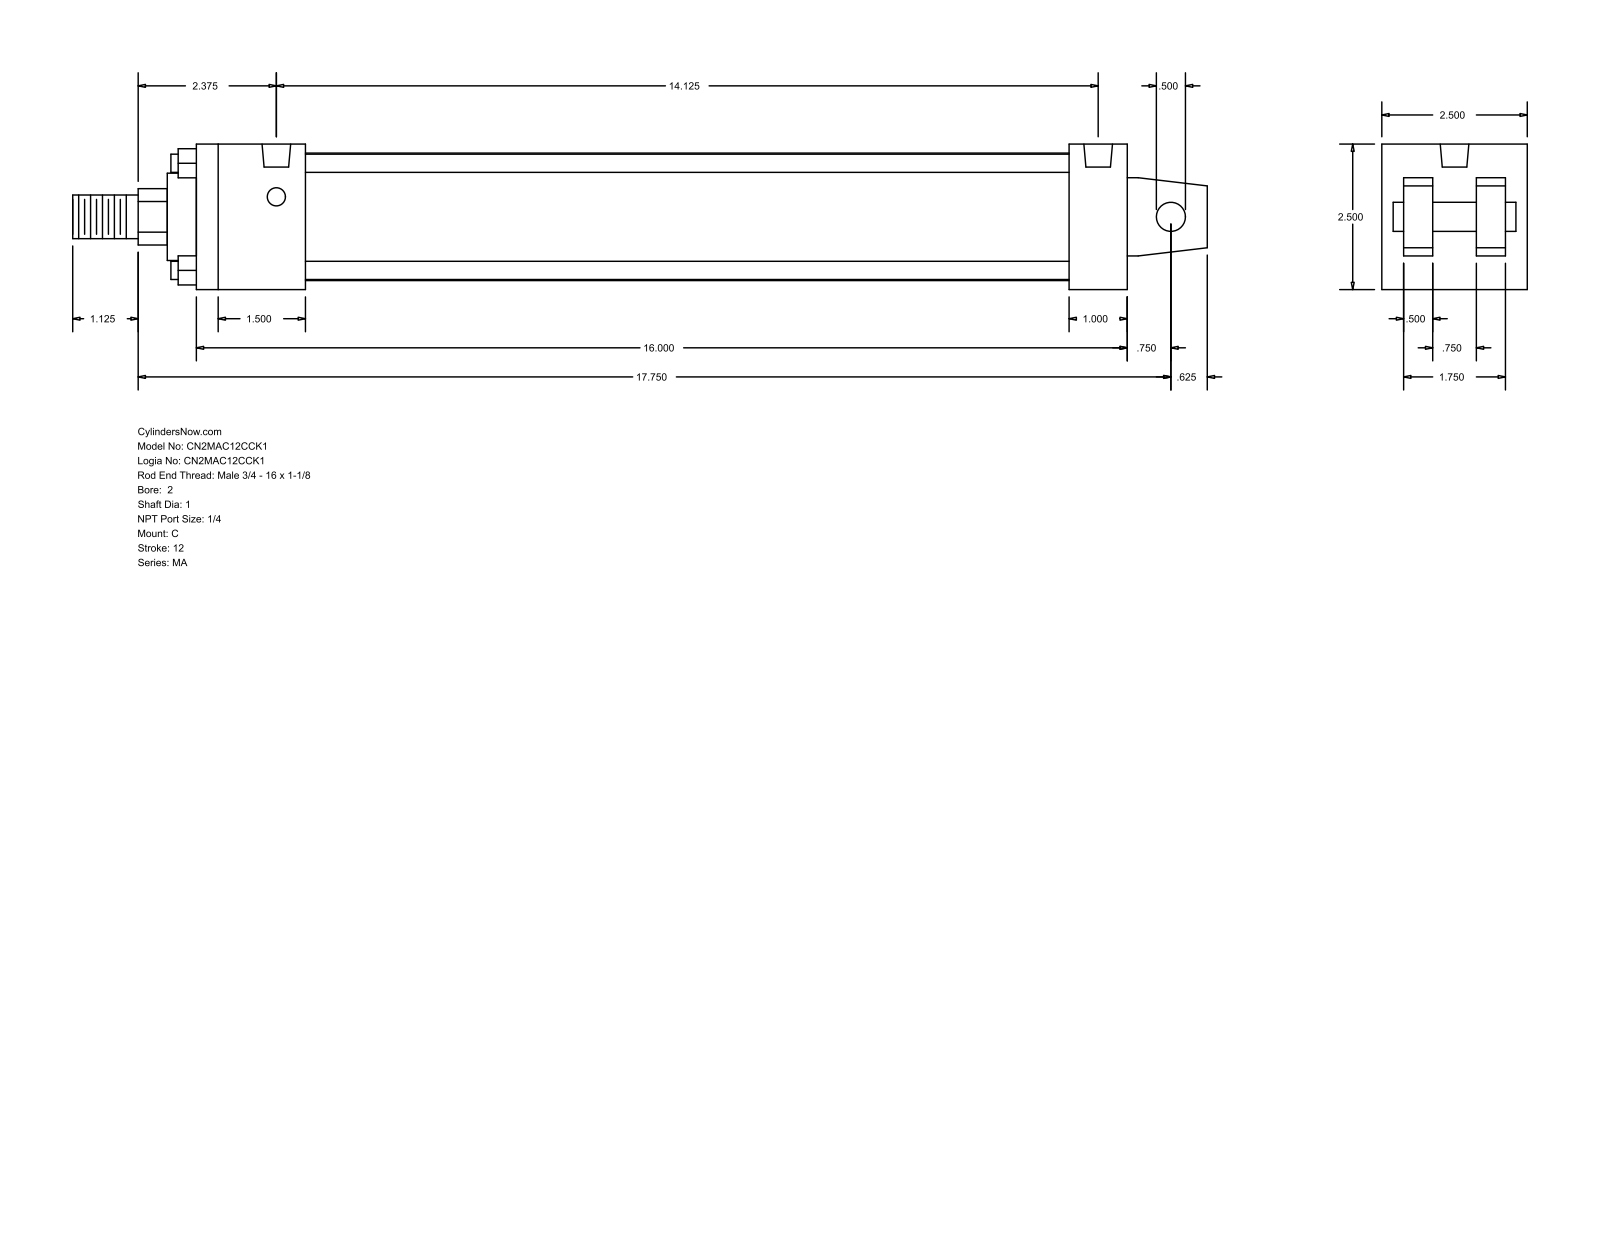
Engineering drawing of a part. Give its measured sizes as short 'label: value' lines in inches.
name: MA_C__0200_1
written by: GSSL Pune (CONFIG_CONTROL_DESIGN)
unit: in
bodies: 0 solids, 103 faces (76 planar, 27 cylindrical, 0 other)
size: 19.5 × 2.5 × 2.5
holes: 4× ⌀0.313, 2× ⌀0.492
bosses: 4× ⌀0.313, 1× ⌀2.19, 1× ⌀1.5, 1× ⌀1, 1× ⌀0.75, 1× ⌀0.5
rounds: 1× R0.484
face distances: 2.5, 0.5, 16, 0.875, 1.625, 0.375, 2.125, 1.25, 1.875, 1
hole spacings: 14.125
